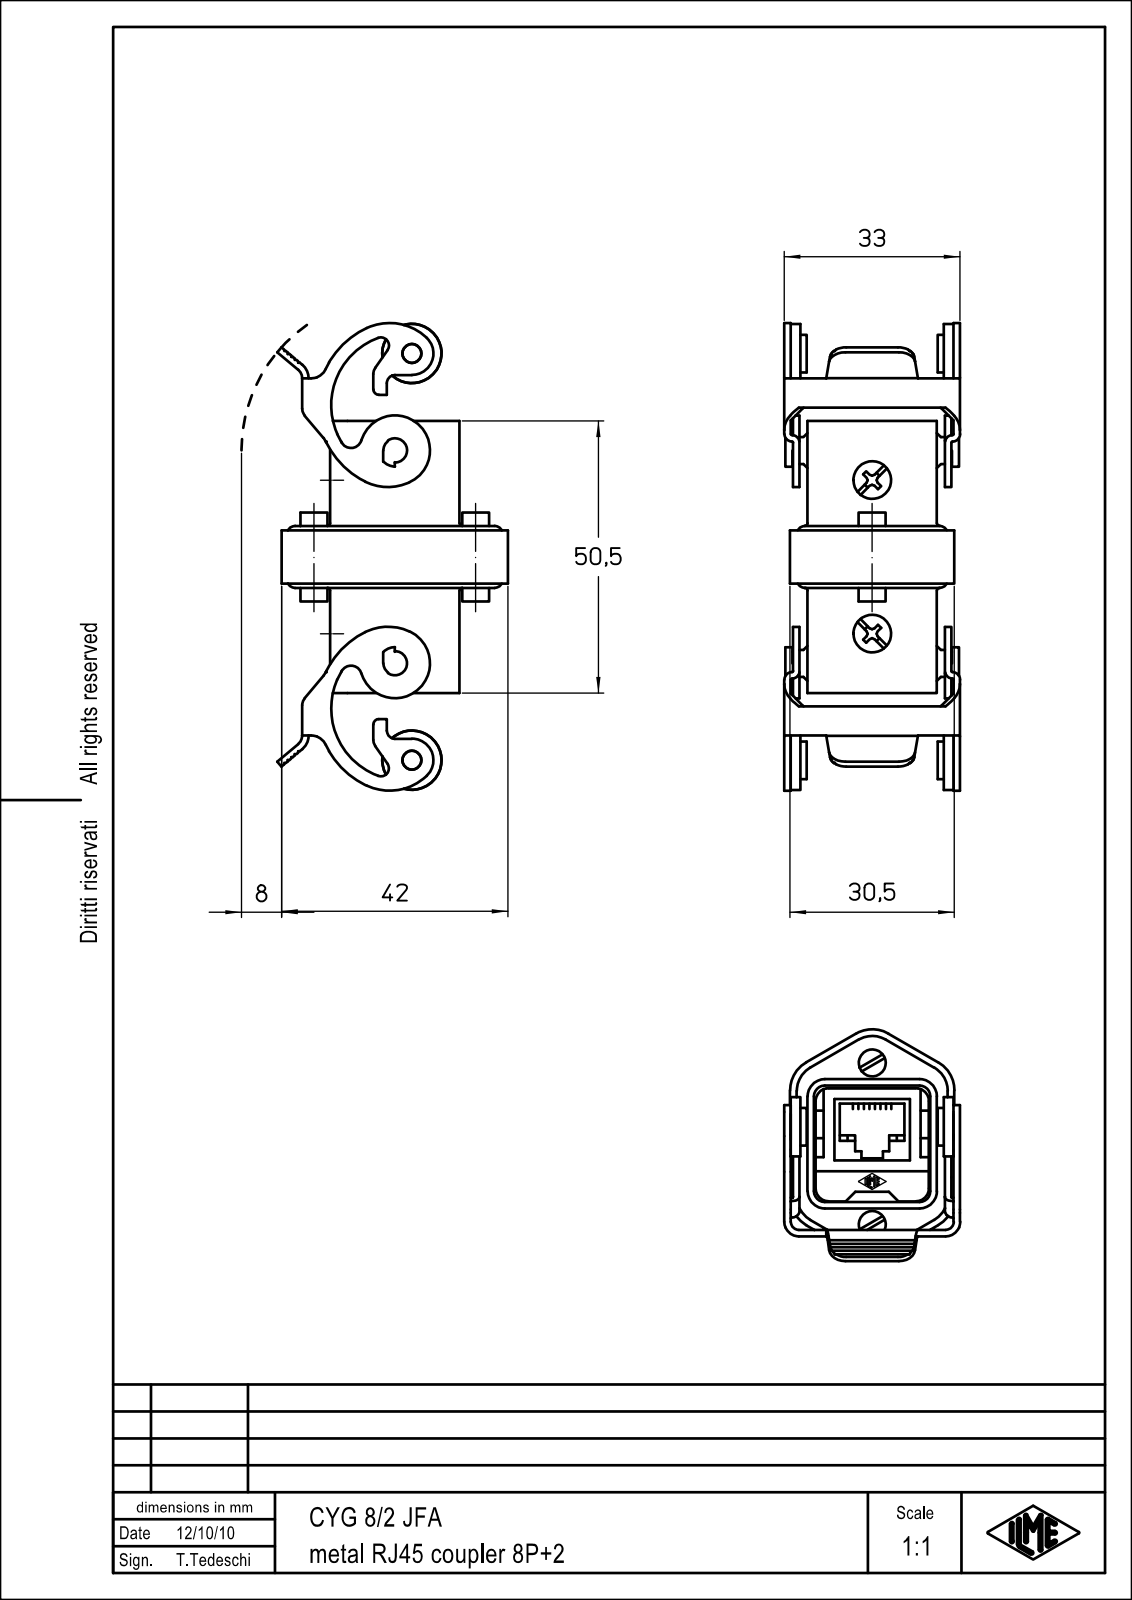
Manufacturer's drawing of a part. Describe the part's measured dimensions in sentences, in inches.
The part is named "CYG_8-2_JFA". Its 3-D file was written by "Creo Elements/Direct Modeling 20.1B 02-Apr-2019 (C) Parametric Technology GmbH (AUTOMOTIVE_DESIGN)". It is 1 solid with 1034 faces: 542 planar, 328 cylindrical and 164 other. Overall it measures 3.512 by 1.671 by 1.362 inches. Its volume is 1.735 cubic inches and its surface area 39.76 square inches. Round holes: 4 of diameter 0.138, 2 of diameter 0.13, 2 of diameter 0.134, 2 of diameter 0.157. Round bosses or shafts: 4 of diameter 0.134, 2 of diameter 0.433, 2 of diameter 0.236, 2 of diameter 0.22, 2 of diameter 0.197, 2 of diameter 0.157, 2 of diameter 0.138, 2 of diameter 0.13. Partial cylindrical surfaces (rounded edges, fillets, slot ends): 24 of radius 0.02, 18 of radius 0.047, 18 of radius 0.079, 16 of radius 0.059, 12 of radius 0.118, 10 of radius 0.008, 8 of radius 0.069, 6 of radius 0.094. The main face-to-face distances are 0.049, 0.896, 0.059, 0.945, 0.886, 0.827, 0.236, 0.177, 0.047, 1.016. The hole center spacings are 0.266, 0.27, 0.445, 0.839, 0.949, 1.009, 1.017, 1.138.
